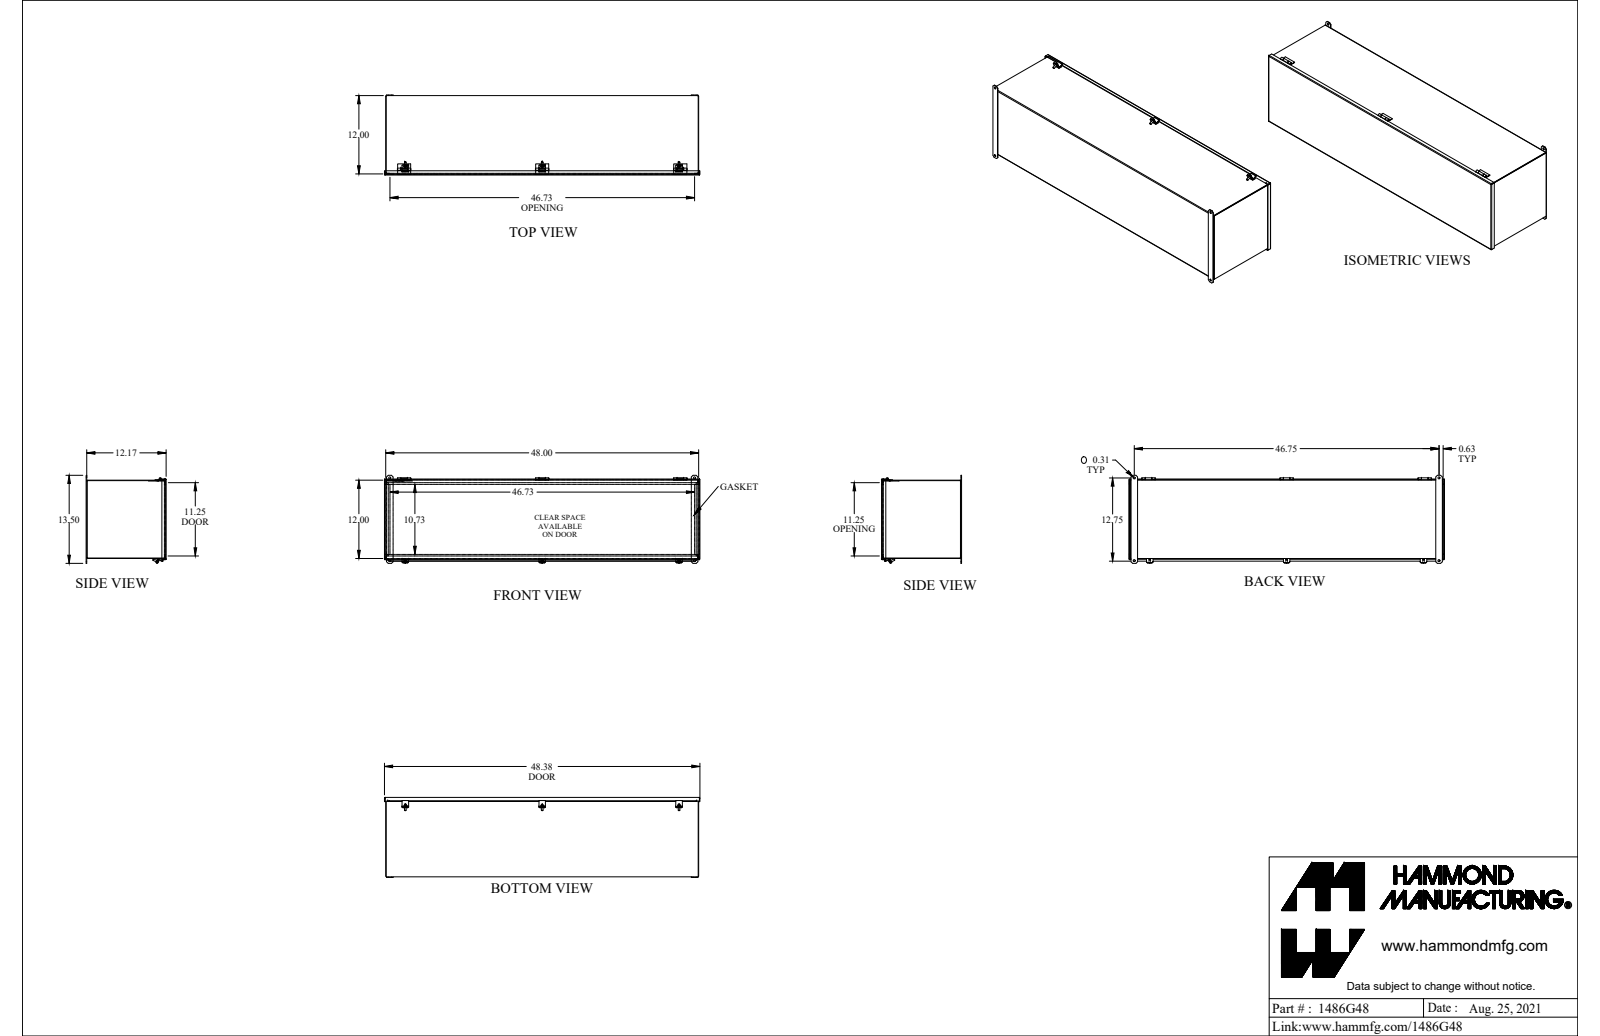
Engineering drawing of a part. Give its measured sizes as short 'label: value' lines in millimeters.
name: 1486G48
written by: SolidWorks 2021 (AUTOMOTIVE_DESIGN)
unit: mm
bodies: 12 solids, 485 faces (327 planar, 129 cylindrical, 29 other)
size: 1228.7 × 342.9 × 311.6
volume: 3 469 000 mm³; area: 3 675 000 mm²
holes: 4× ⌀8, 3× ⌀5.4, 1× ⌀4.7
bosses: 3× ⌀12.2, 3× ⌀6.2, 1× ⌀8.6, 1× ⌀4.6
rounds: 8× R1, 8× R2.8, 6× R0.3, 6× R0.8, 6× R3.6, 6× R4.8, 5× R0.9, 5× R2.7
face distances: 1.8, 303, 1.8, 1.8, 304.8, 301.2, 307.4, 305.6, 309.2, 307.3
hole spacings: 322.3, 533.4, 1187.5, 1230.4, 1066.8
